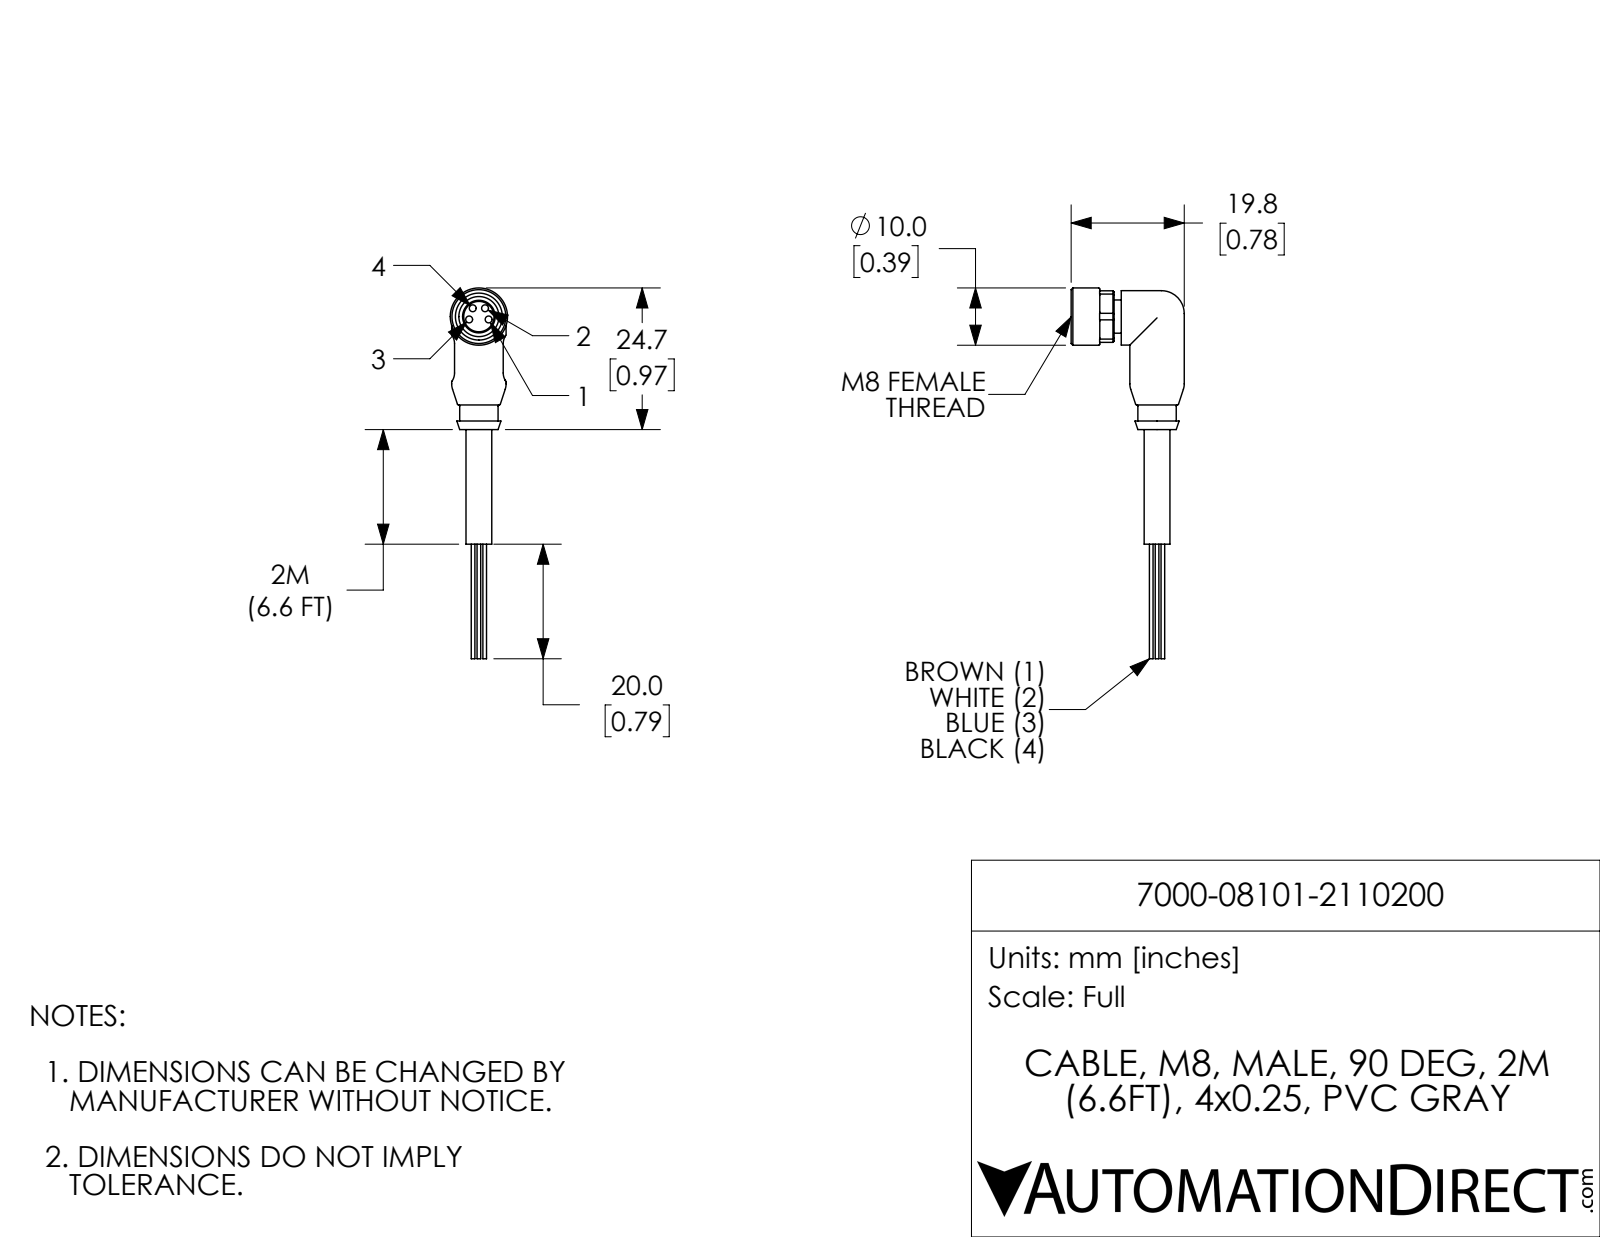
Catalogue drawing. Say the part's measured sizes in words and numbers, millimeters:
The part is named "7000-08101-2110200". Its 3-D file was written by "SolidWorks 2017 (AUTOMOTIVE_DESIGN)". It is 5 solids with 117 faces: 41 planar, 47 cylindrical and 29 other. Overall it measures 64.7 by 19.8 by 10 millimeters. Its volume is 2 410 cubic millimeters and its surface area 1 920 square millimeters. Round holes: 4 of diameter 1.2, 1 of diameter 7. Round bosses or shafts: 3 of diameter 0.6, 2 of diameter 9.5, 1 of diameter 10, 1 of diameter 6.7, 1 of diameter 5.8, 1 of diameter 5.7, 1 of diameter 4.5, 1 of diameter 0.6. Partial cylindrical surfaces (rounded edges, fillets, slot ends): 4 of radius 0.2, 4 of radius 2.5, 1 of radius 4.9. The main face-to-face distances are 1.2, 9, 1.5, 8.5, 0.7, 20, 6.8, 8.1, 7.5, 8.7. The hole center spacings are 1.8, 1.8, 2.1, 3.4, 2.1, 3.4.
